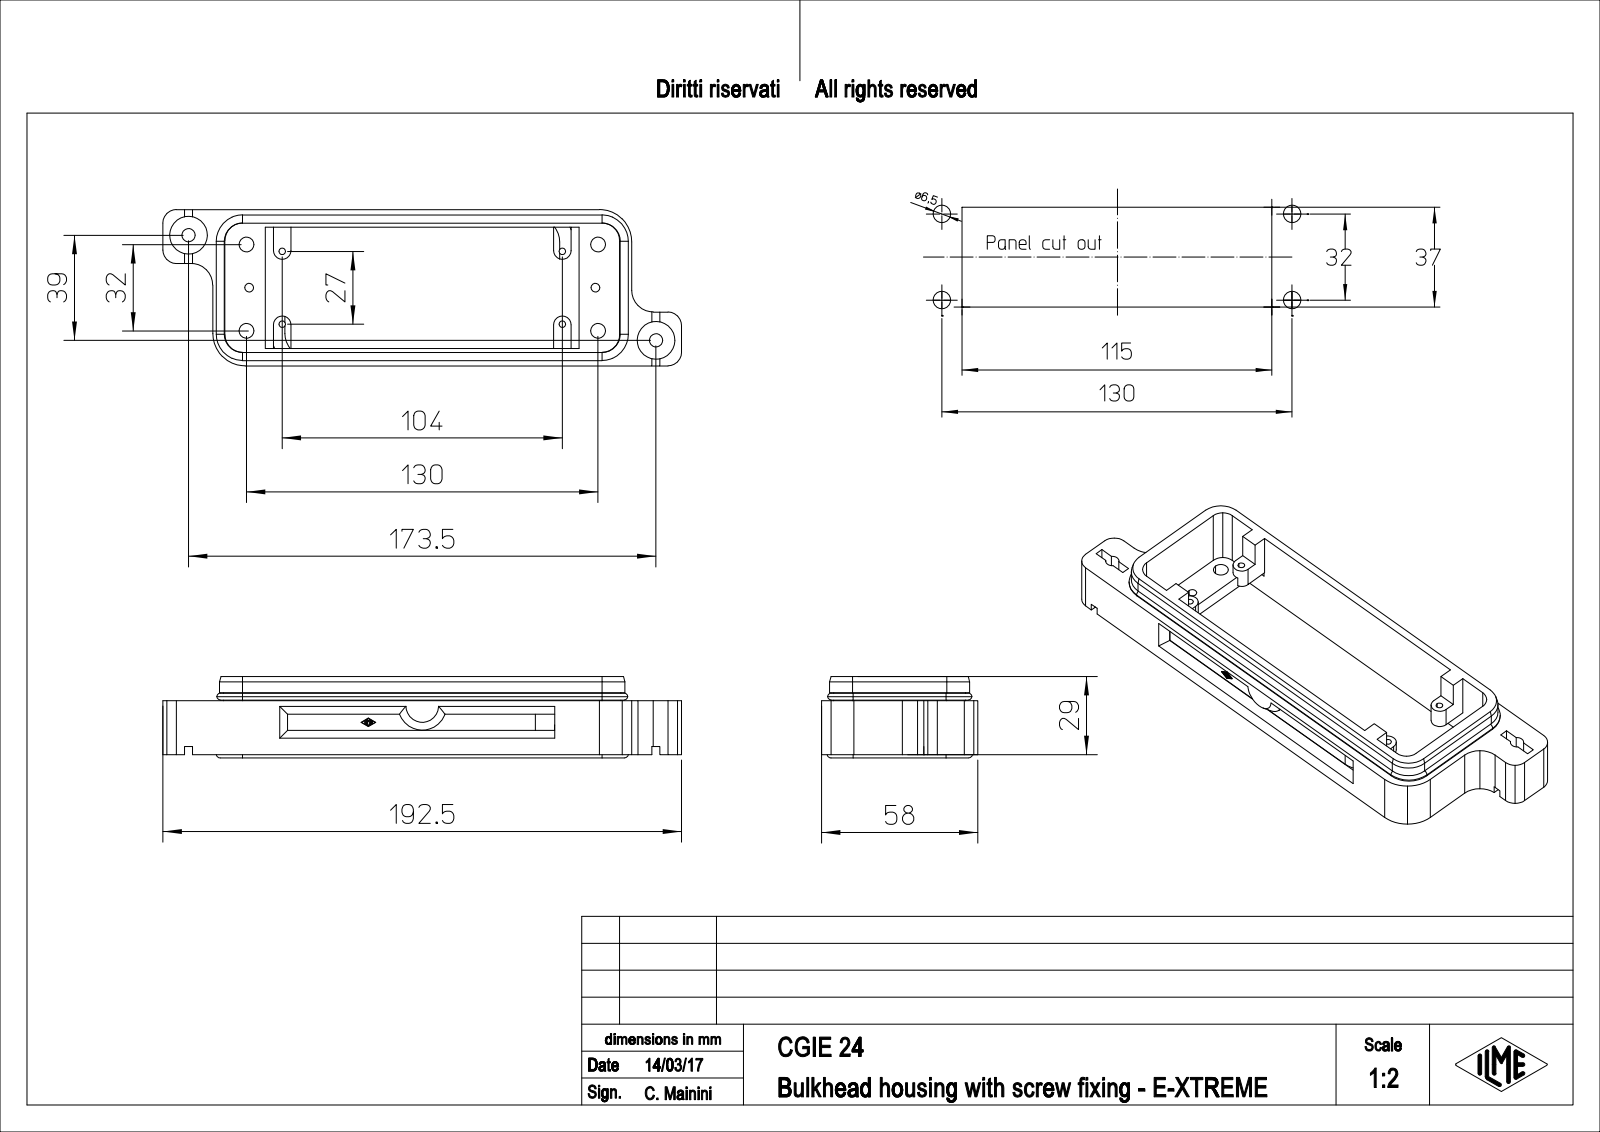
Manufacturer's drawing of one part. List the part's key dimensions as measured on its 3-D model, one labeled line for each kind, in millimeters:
Part name (STEP PRODUCT): CGIE_24
STEP written by: PTC Creo Elements/Direct Modeling 19.0E 27-Jun-2016 (C) Parametric Technology GmbH (AUTOMOTIVE_DESIGN)
Units: millimetres
Bodies: 1 solid, 310 faces (164 planar, 120 cylindrical, 26 other)
Overall size (bounding box): 192.5 × 58 × 30.25
Volume: 80 528 mm³ · Surface area: 42 734 mm²
Round holes (diameter × count): ⌀2.46 ×4, ⌀5.5 ×4, ⌀3.24 ×2, ⌀4.92 ×2, ⌀14 ×2
Round bosses / shafts (diameter × count): ⌀2.5 ×4, ⌀3 ×2
Partial cylindrical surfaces — rounded edges, fillets, slot ends (radius × count): R0.1 ×14, R5 ×8, R3.25 ×4, R6.5 ×4, R7 ×4, R8.5 ×4, R9.5 ×4, R1.5 ×2
Main face-to-face distances: 6.5, 51.5, 3, 45, 20, 48.5, 3.5, 55, 58, 9
Hole centre spacings: 13.48, 16.03, 18.23, 32.34, 117.03, 117.28, 120.9, 130.48
